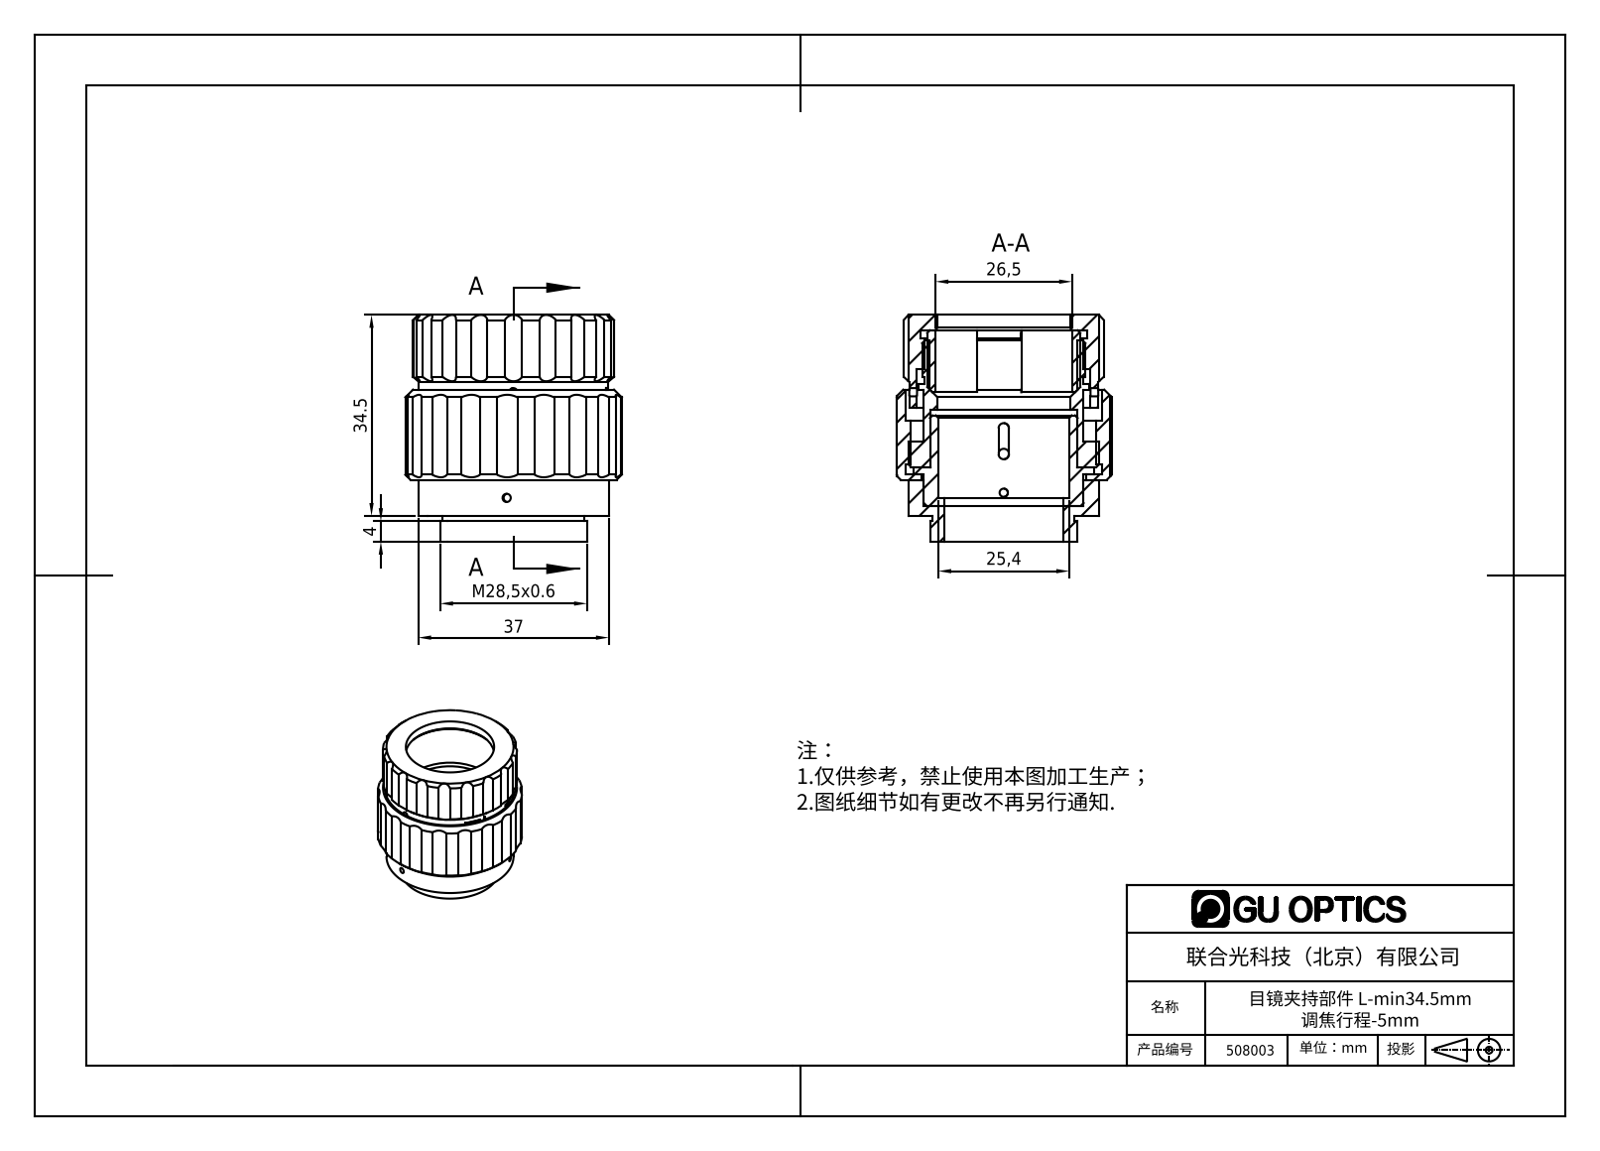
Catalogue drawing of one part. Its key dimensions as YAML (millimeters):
part_name: "508003"
step_written_by: "SolidWorks 2020 (CONFIG_CONTROL_DESIGN)"
units: millimeters
bodies: {solids: 6, faces: 254, planar: 35, cylindrical: 178, other: 41}
overall_size: [44, 42, 41.98]
volume: 25356
surface_area: 26799
round_holes:
  - {diameter: 1.6, count: 7}
  - {diameter: 2.05, count: 1}
  - {diameter: 23, count: 1}
  - {diameter: 23.2, count: 1}
  - {diameter: 25.4, count: 1}
  - {diameter: 25.7, count: 1}
  - {diameter: 26.5, count: 1}
  - {diameter: 28.65, count: 1}
  - {diameter: 28.7, count: 1}
  - {diameter: 30.7, count: 1}
  - {diameter: 32, count: 1}
  - {diameter: 32.2, count: 1}
round_bosses_or_shafts:
  - {diameter: 37, count: 1}
  - {diameter: 36.7, count: 1}
  - {diameter: 35, count: 1}
  - {diameter: 33.2, count: 1}
  - {diameter: 31.7, count: 1}
  - {diameter: 31, count: 1}
  - {diameter: 29.7, count: 1}
  - {diameter: 28.5, count: 1}
partial_cylinders:
  - {radius: 2, count: 18}
  - {radius: 5, count: 18}
  - {radius: 1, count: 2}
  - {radius: 19.5, count: 1}
  - {radius: 21, count: 1}
face_to_face_distances: [5, 7.5, 6, 14.5, 2, 7, 2.5, 1, 1.5, 29.5]
